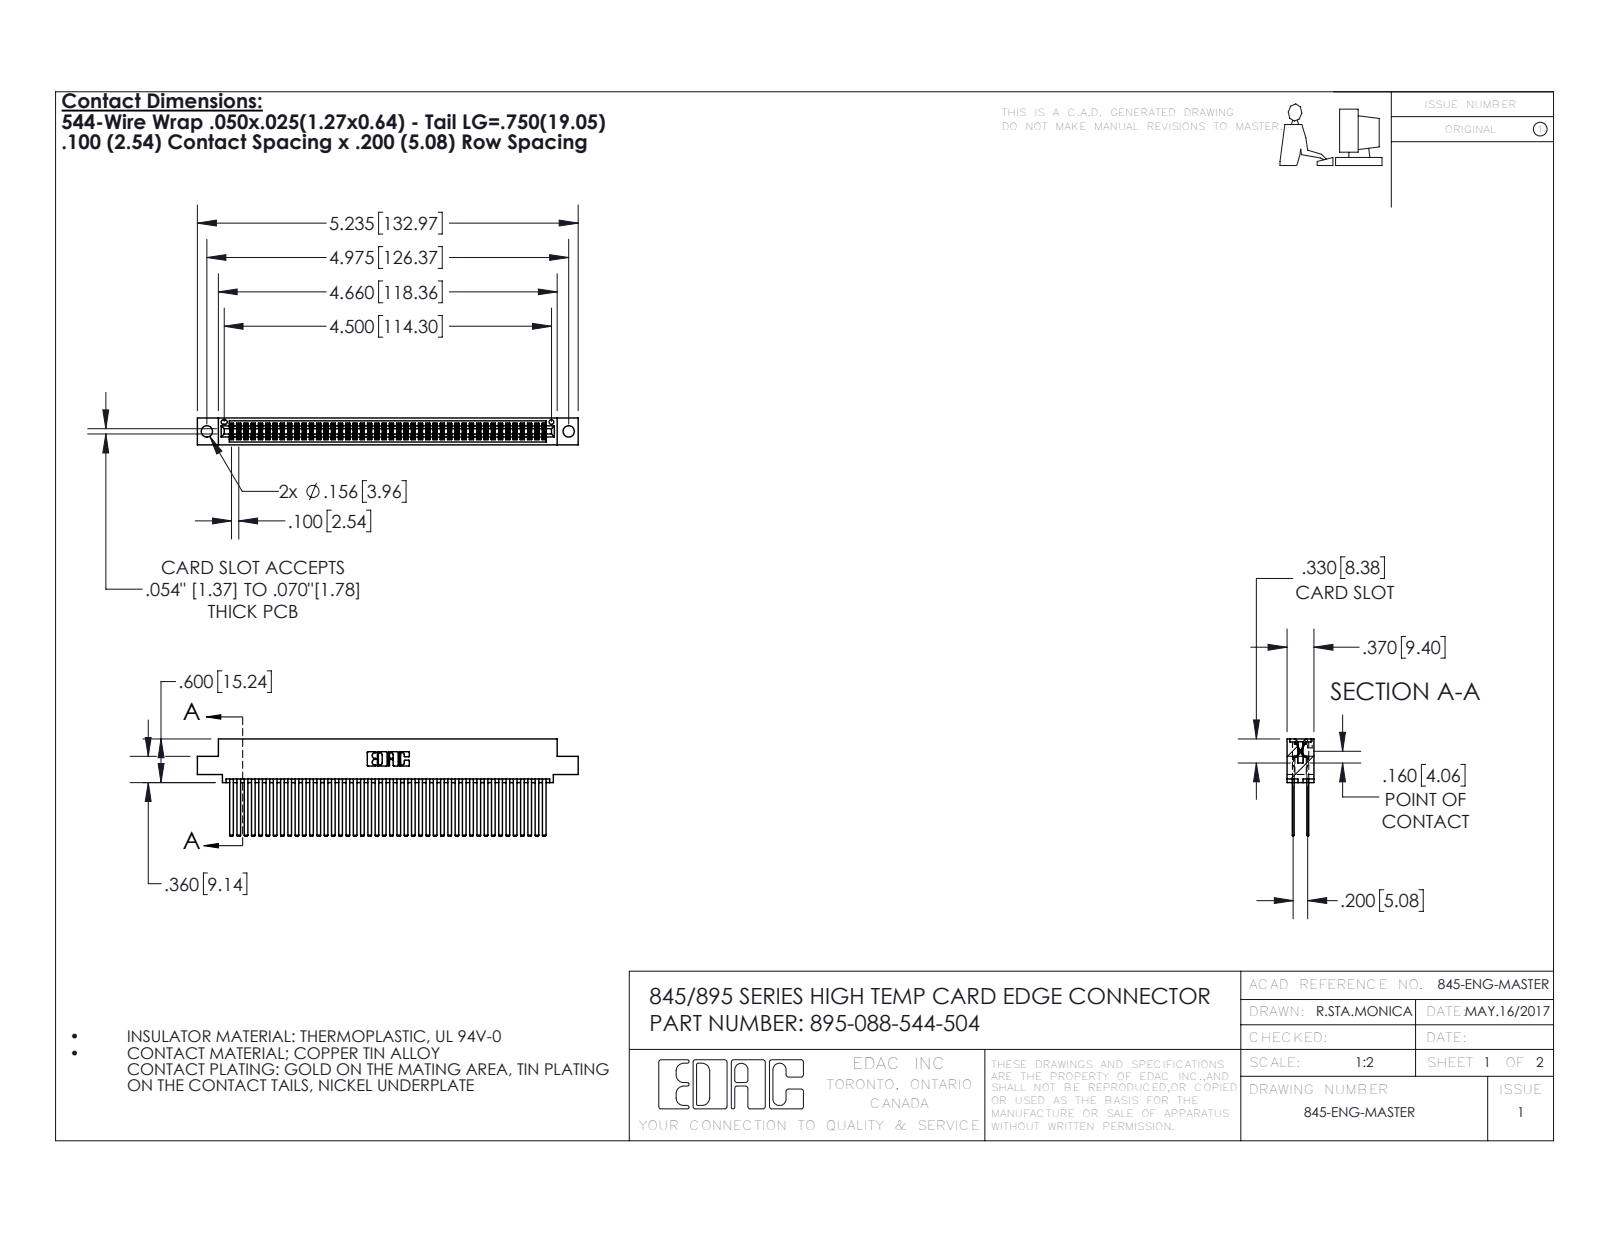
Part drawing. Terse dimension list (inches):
name: 395-088-544-504; 345-292-001_345-293-144; 345 Part_0.110 Offset - 0.156 Dia-TH
written by: SolidWorks 2016 (CONFIG_CONTROL_DESIGN)
unit: in
bodies: 89 solids, 4002 faces (2636 planar, 1366 cylindrical, 0 other)
size: 5.235 × 1.337 × 0.37
volume: 0.855 in³; area: 37.62 in²
holes: 2× ⌀0.156, 1× ⌀0.064
rounds: 132× R0.006, 22× R0.01, 6× R0.007, 6× R0.031, 3× R0.026, 2× R0.014, 2× R0.019, 2× R0.022
face distances: 0.2, 0.025, 0.298, 0.072, 0.098, 0.272, 0.225, 0.175, 0.37, 0.05
hole spacings: 0.27, 4.739, 4.975
